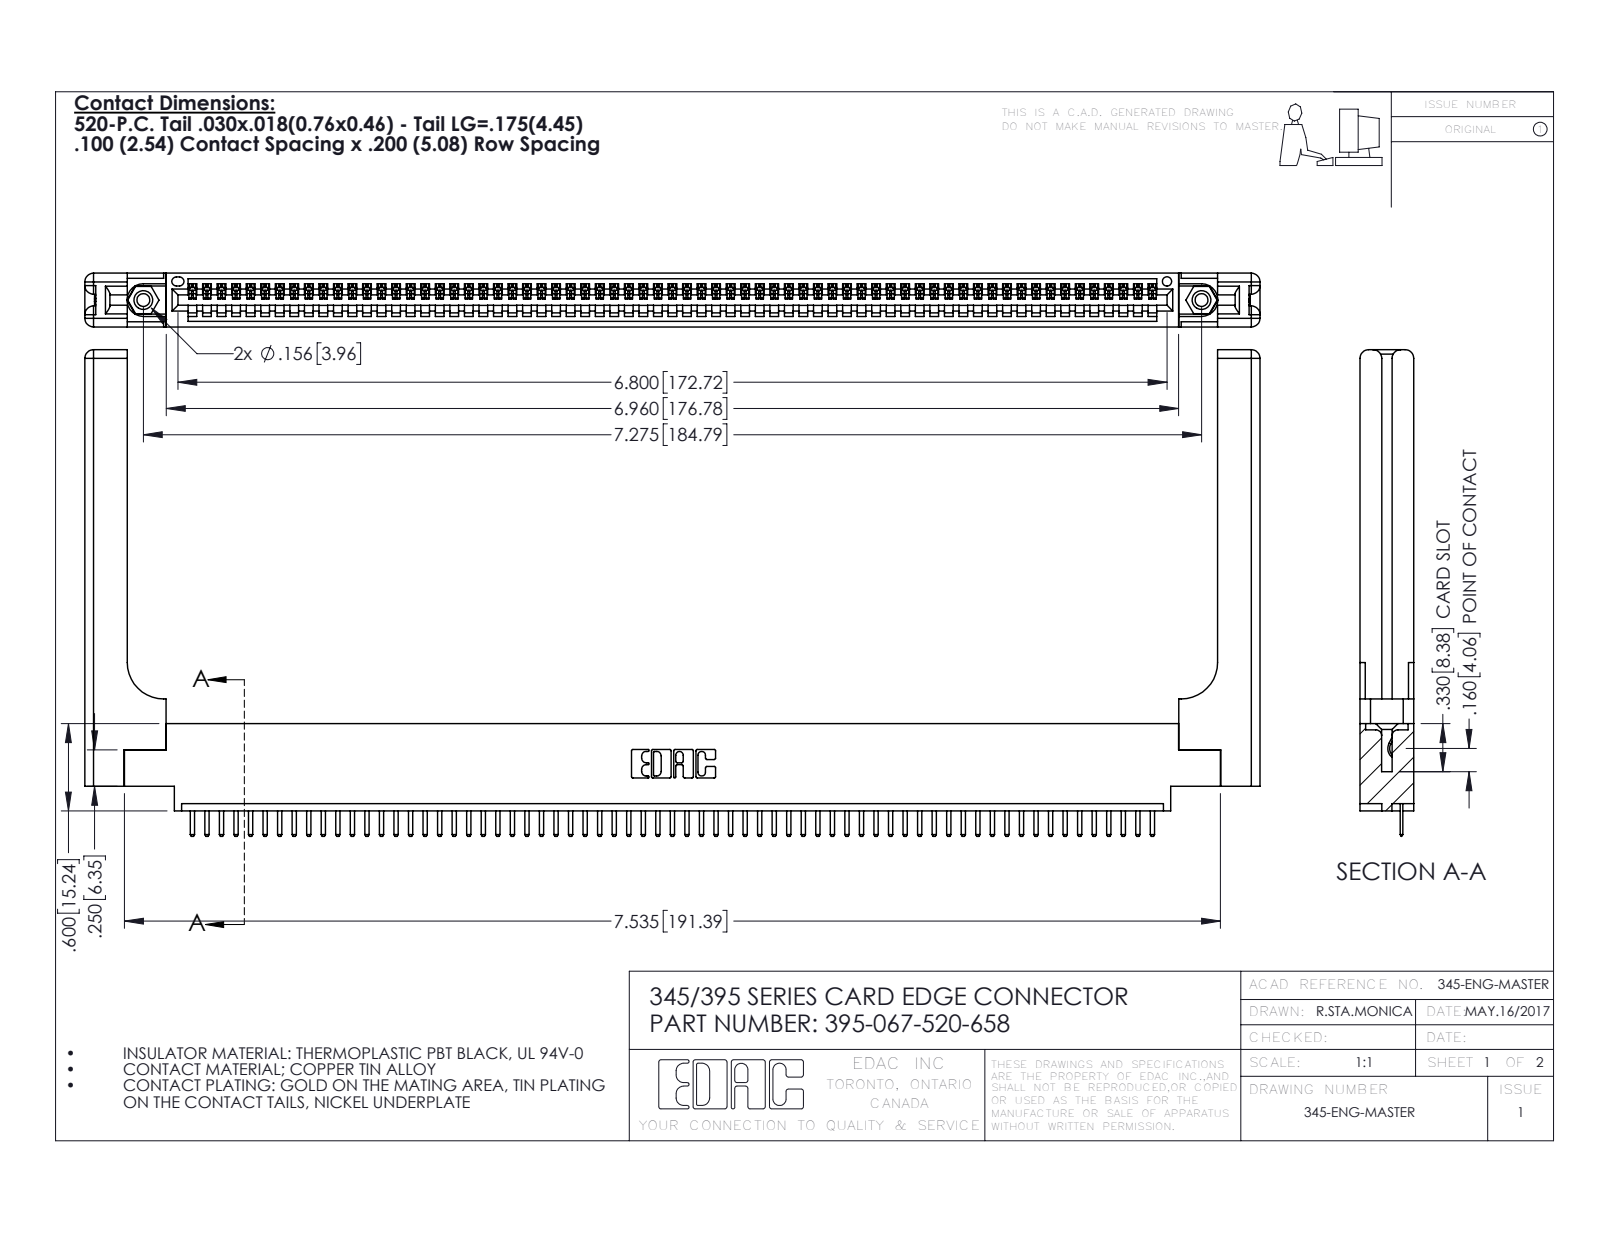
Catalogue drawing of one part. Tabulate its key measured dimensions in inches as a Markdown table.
| quantity | value |
| --- | --- |
| part name | 395-067-520-658; 345-220-058_345-220-058; 345-250-001_345-250-001-102; 345-292-001_345-293-120 (+1 more) |
| STEP written by | SolidWorks 2016 (CONFIG_CONTROL_DESIGN) |
| units | inches |
| bodies | 72 solids, 4540 faces (3046 planar, 1434 cylindrical, 60 other) |
| overall size | 8.079 × 3.345 × 0.37 |
| volume | 1.702 in³ |
| surface area | 47.91 in² |
| round holes (diameter × count) | 0.089 × 2, 0.125 × 2, 0.156 × 2, 0.064 × 1 |
| round bosses / shafts (diameter × count) | 0.155 × 2 |
| partial cylindrical surfaces (radius × count) | 0.01 × 136, 0.006 × 134, 0.01 × 22, 0.06 × 16, 0.007 × 6, 0.031 × 6, 0.026 × 3, 0.03 × 2 |
| main face-to-face distances | 0.37, 0.072, 0.298, 0.098, 0.272, 0.025, 0.2, 0.225, 0.148, 0.15 |
| hole center spacings | 0.27, 7.039, 7.275 |
